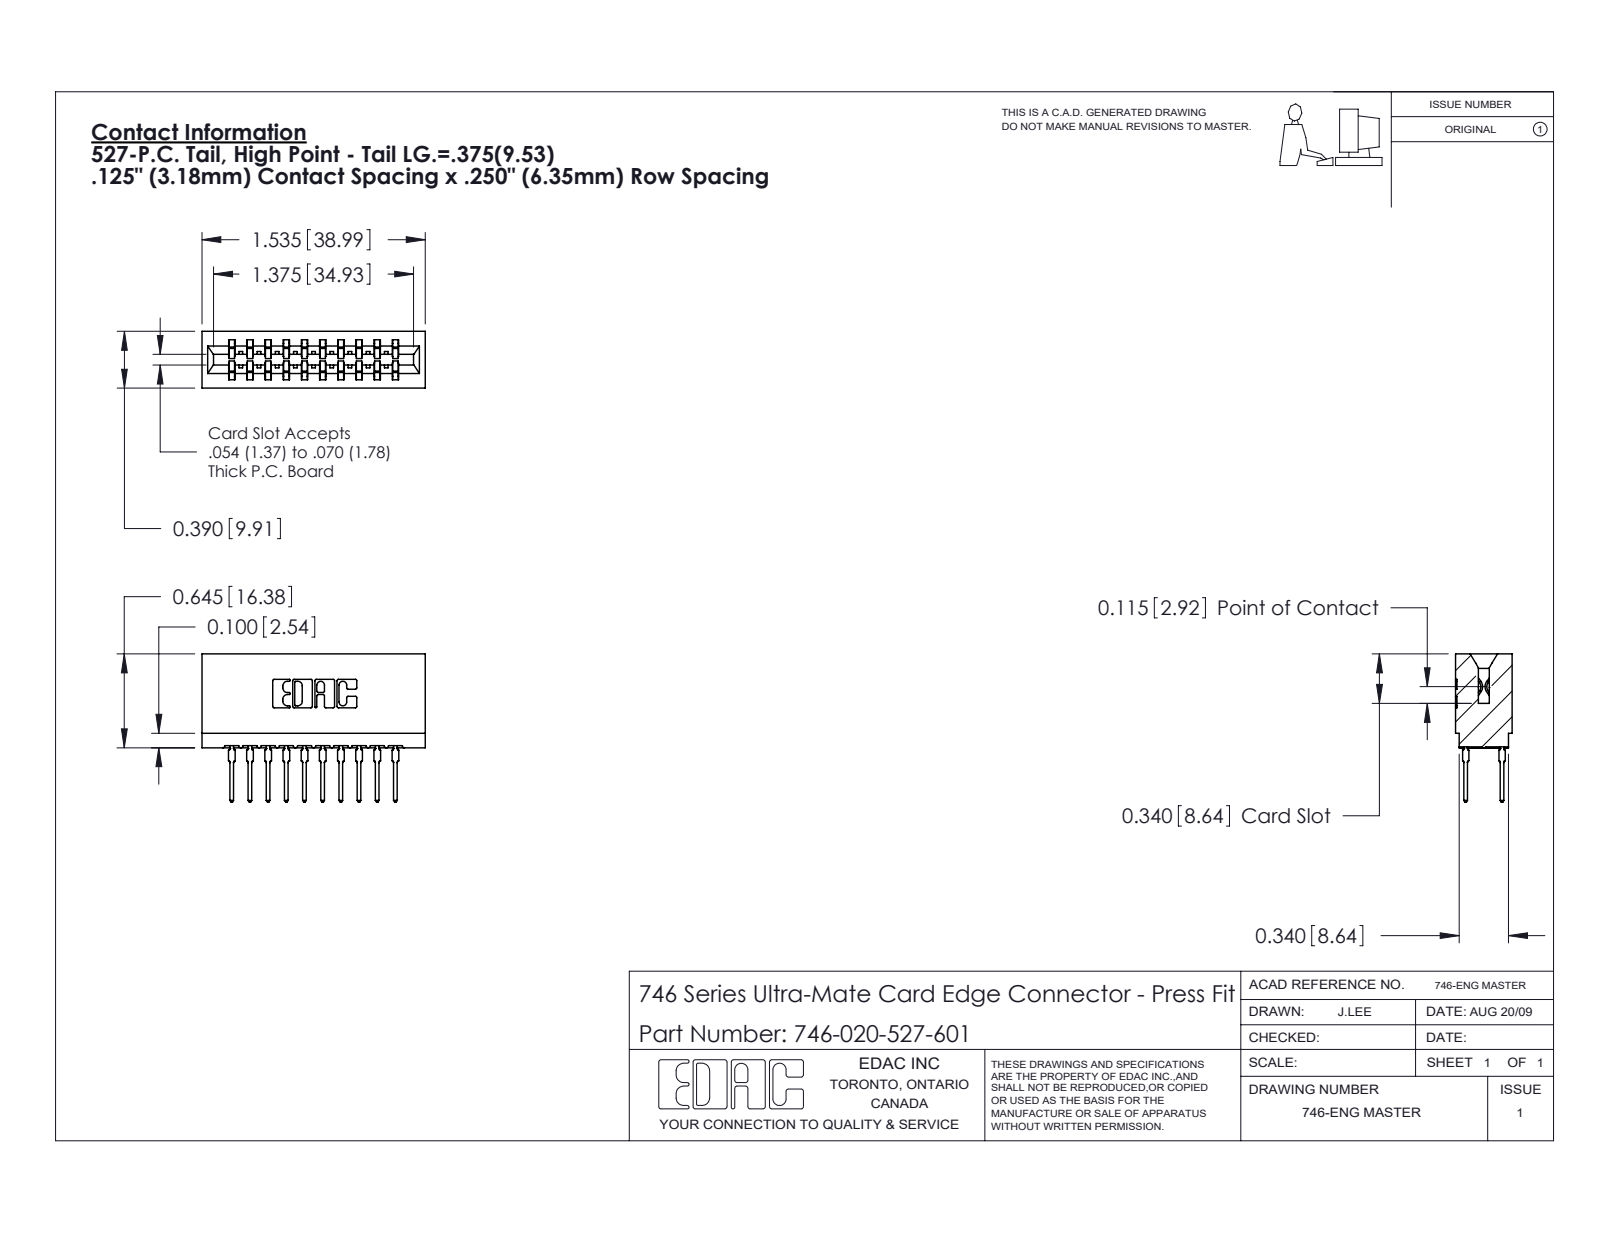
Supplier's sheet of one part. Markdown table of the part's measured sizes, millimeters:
| quantity | value |
| --- | --- |
| part name | 746-020-527-601; 746-292-001_527; 746 Part_.340 Slot Depth - 01 |
| STEP written by | SolidWorks 2020 (CONFIG_CONTROL_DESIGN) |
| units | millimeters |
| bodies | 21 solids, 1887 faces (975 planar, 392 cylindrical, 520 other) |
| overall size | 39 × 25.9 × 9.9 |
| volume | 4 700 mm³ |
| surface area | 6 465 mm² |
| partial cylindrical surfaces (radius × count) | 0.5 × 40, 0.3 × 22, 0.4 × 11, 0.1 × 8, 0.3 × 8, 0.2 × 6, 0.8 × 6, 0.7 × 3 |
| main face-to-face distances | 6.4, 12.7, 1.4, 8.5, 1.1, 3.2, 7.4, 9.5, 3.2, 9.9 |
